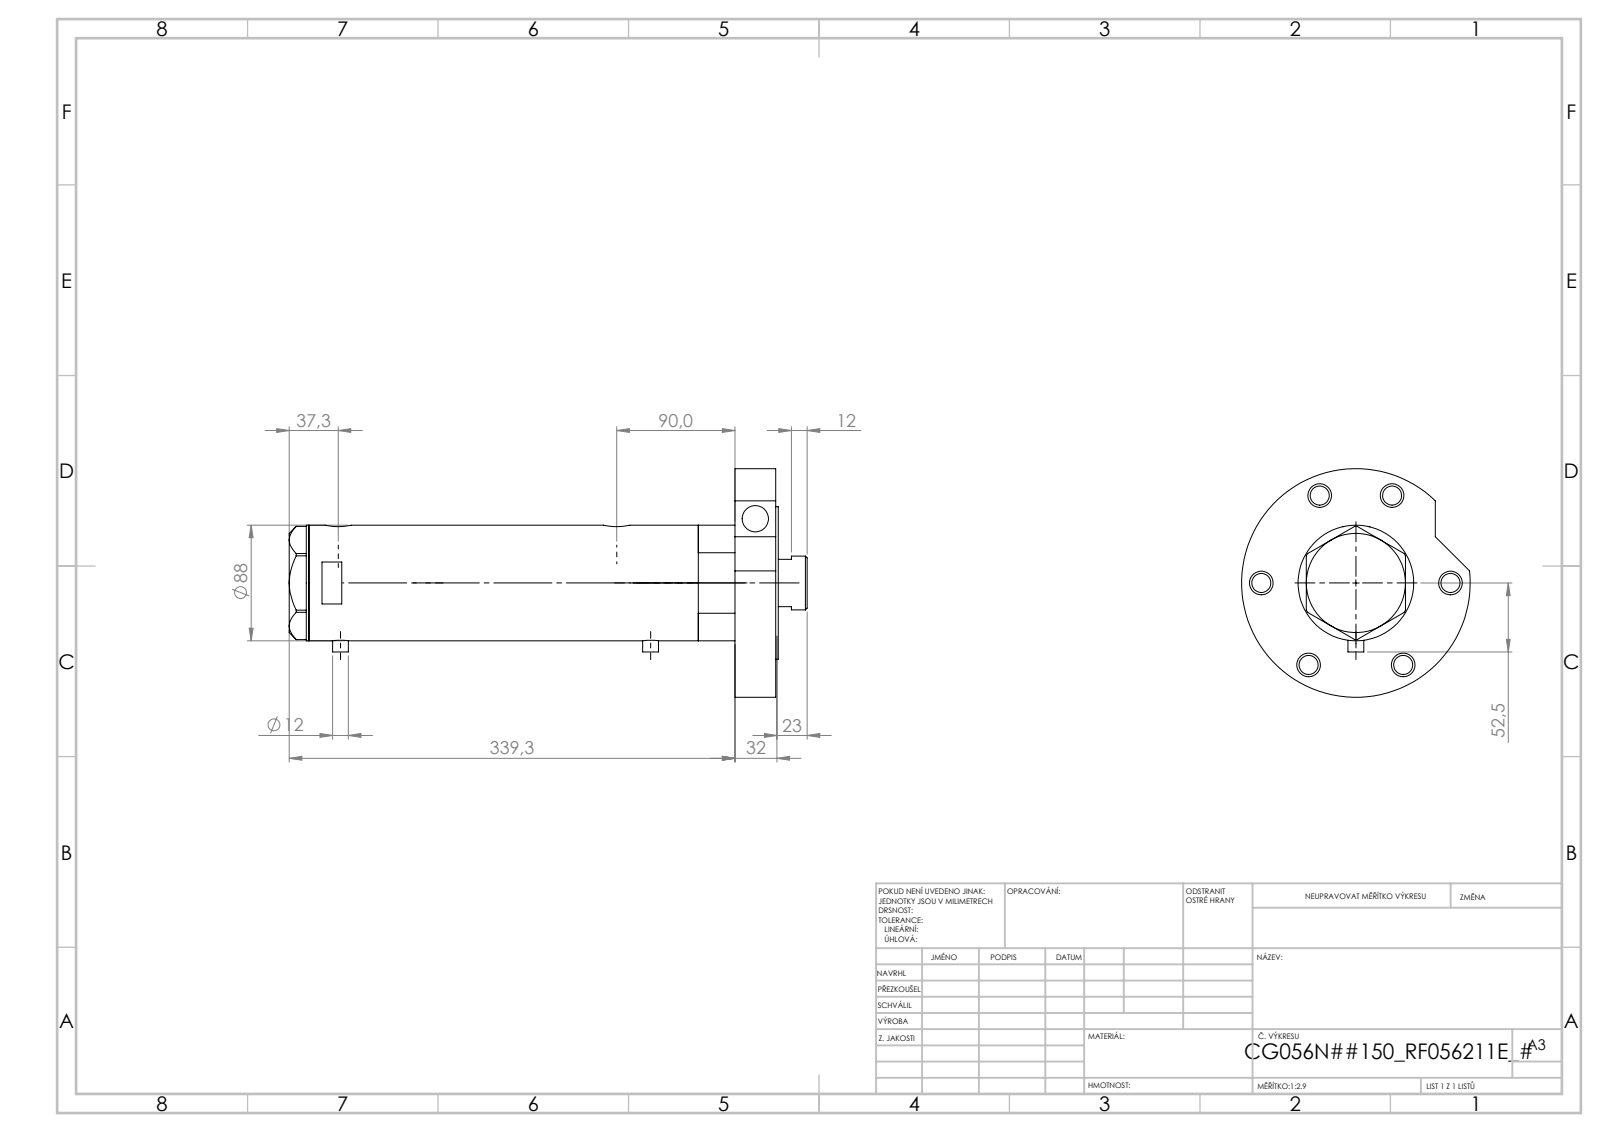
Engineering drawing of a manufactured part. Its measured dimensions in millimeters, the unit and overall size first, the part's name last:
Units: millimetres
Overall size (bounding box): 394.3 × 174 × 174
Round holes (diameter × count): ⌀14.5 ×7, ⌀18 ×6, ⌀20 ×3, ⌀12.5 ×2, ⌀13.16 ×2, ⌀42 ×1, ⌀43.5 ×1, ⌀56 ×1, ⌀60 ×1, ⌀75 ×1, ⌀80 ×1
Round bosses / shafts (diameter × count): ⌀12 ×2, ⌀174 ×1, ⌀116 ×1, ⌀88 ×1, ⌀73 ×1, ⌀41 ×1
Main face-to-face distances: 31, 2, 357.3, 324.3, 355.3, 33, 234.4, 89.9, 120.9, 122.9
Hole centre spacings: 72, 80, 119.73, 124.71, 129.15, 143.69, 1.7, 25.8
Volume: 2 554 000 mm³ · Surface area: 357 536 mm²
Bodies: 5 solids, 165 faces (63 planar, 82 cylindrical, 20 other)
Part name (STEP PRODUCT): V270CG_BACK; V270CG_MIDDLE; V270CG_VC; V270CG_RF211E (+1 more)
STEP written by: SolidWorks 2019 (CONFIG_CONTROL_DESIGN)
